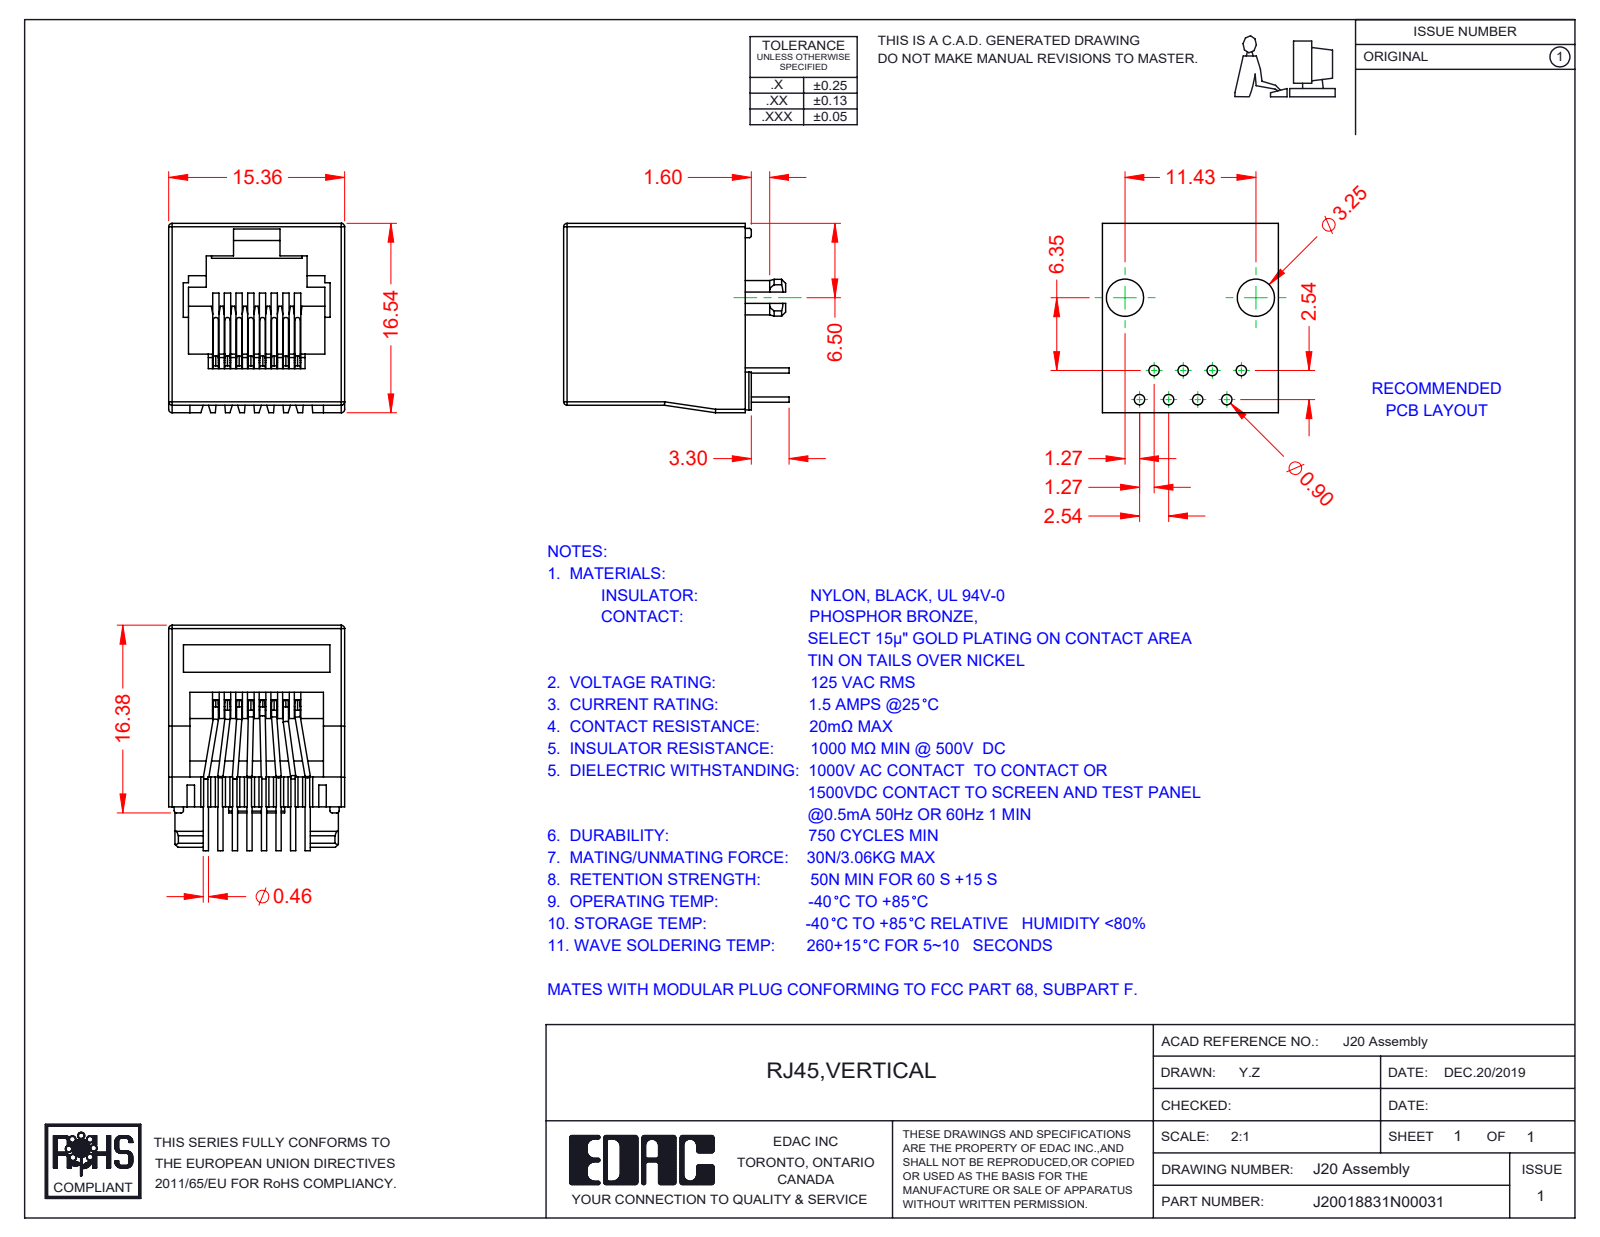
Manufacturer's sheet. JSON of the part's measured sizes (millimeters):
{"part_name": "RJ20018831N00031; 20 Contacts; 20 Insulator", "step_written_by": "SolidWorks 2016 (CONFIG_CONTROL_DESIGN)", "units": "millimeters", "bodies": {"solids": 9, "faces": 573, "planar": 332, "cylindrical": 193, "other": 48}, "overall_size": [19.68, 16.54, 15.36], "volume_mm3": 1935, "surface_area_mm2": 3110, "round_holes": [[2, 2]], "round_bosses_or_shafts": [[0.46, 45]], "partial_cylinders_radius": [[0.13, 16], [0.3, 13], [0.25, 9], [0.2, 5], [0.15, 2], [1.5, 2], [1.6, 2]], "face_to_face_distances": [15.36, 1.73, 2, 13.63, 0.45, 15.85, 1.28, 10.35, 1.5, 14.08], "hole_center_spacings": [11.43]}
